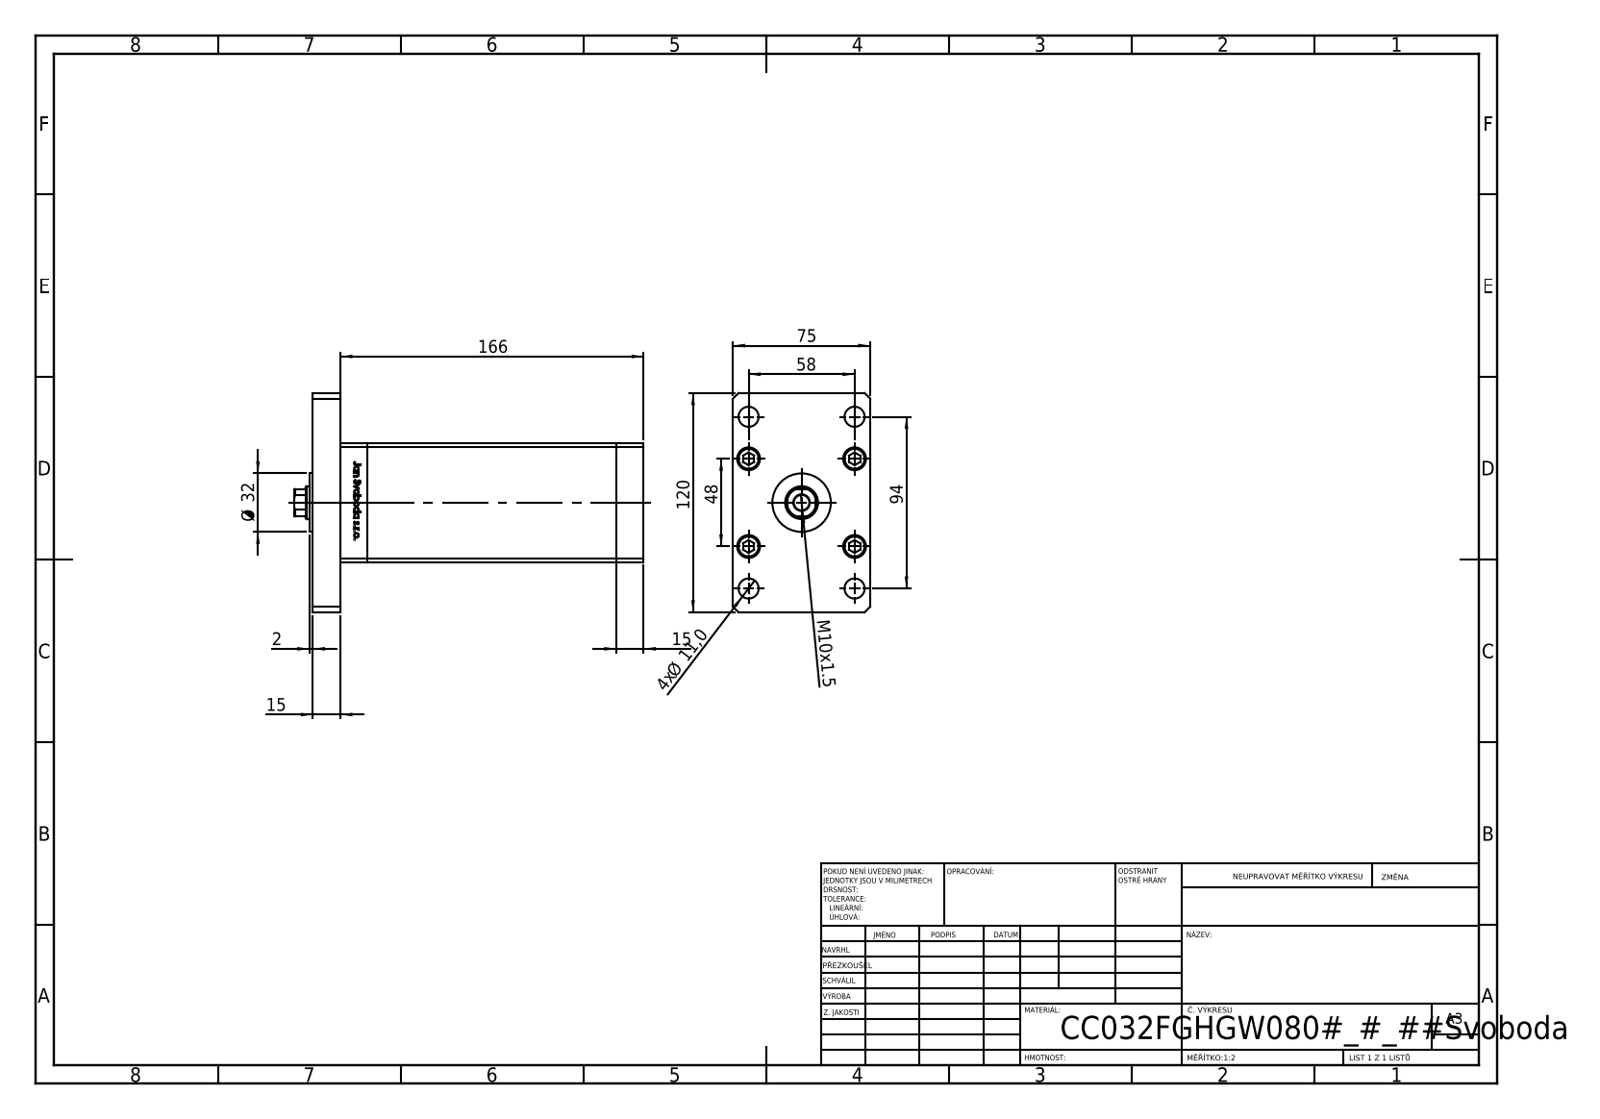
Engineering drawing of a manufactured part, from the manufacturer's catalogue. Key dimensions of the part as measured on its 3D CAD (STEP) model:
Part name (STEP PRODUCT): V220C BACK_F; V220C_VC_F; V220C_F; V220C_F_MIDDLE (+2 more)
STEP written by: SolidWorks 2019 (CONFIG_CONTROL_DESIGN)
Units: millimetres
Bodies: 19 solids, 1308 faces (515 planar, 187 cylindrical, 606 other)
Overall size (bounding box): 191 × 120 × 75
Volume: 848 554 mm³ · Surface area: 159 946 mm²
Round holes (diameter × count): ⌀9 ×5, ⌀13.5 ×5, ⌀8 ×4, ⌀11 ×4, ⌀12.5 ×4, ⌀2 ×2, ⌀13.16 ×2, ⌀8.5 ×1, ⌀18 ×1, ⌀19.5 ×1
Round bosses / shafts (diameter × count): ⌀12.5 ×5, ⌀8 ×5, ⌀32 ×1
Partial cylindrical surfaces — rounded edges, fillets, slot ends (radius × count): R0.93 ×2, R8.5 ×1
Main face-to-face distances: 15, 75, 151, 166, 65, 30, 136, 181, 13, 153
Hole centre spacings: 24, 23, 37.64, 55.23, 58, 62.39, 71, 91.68
